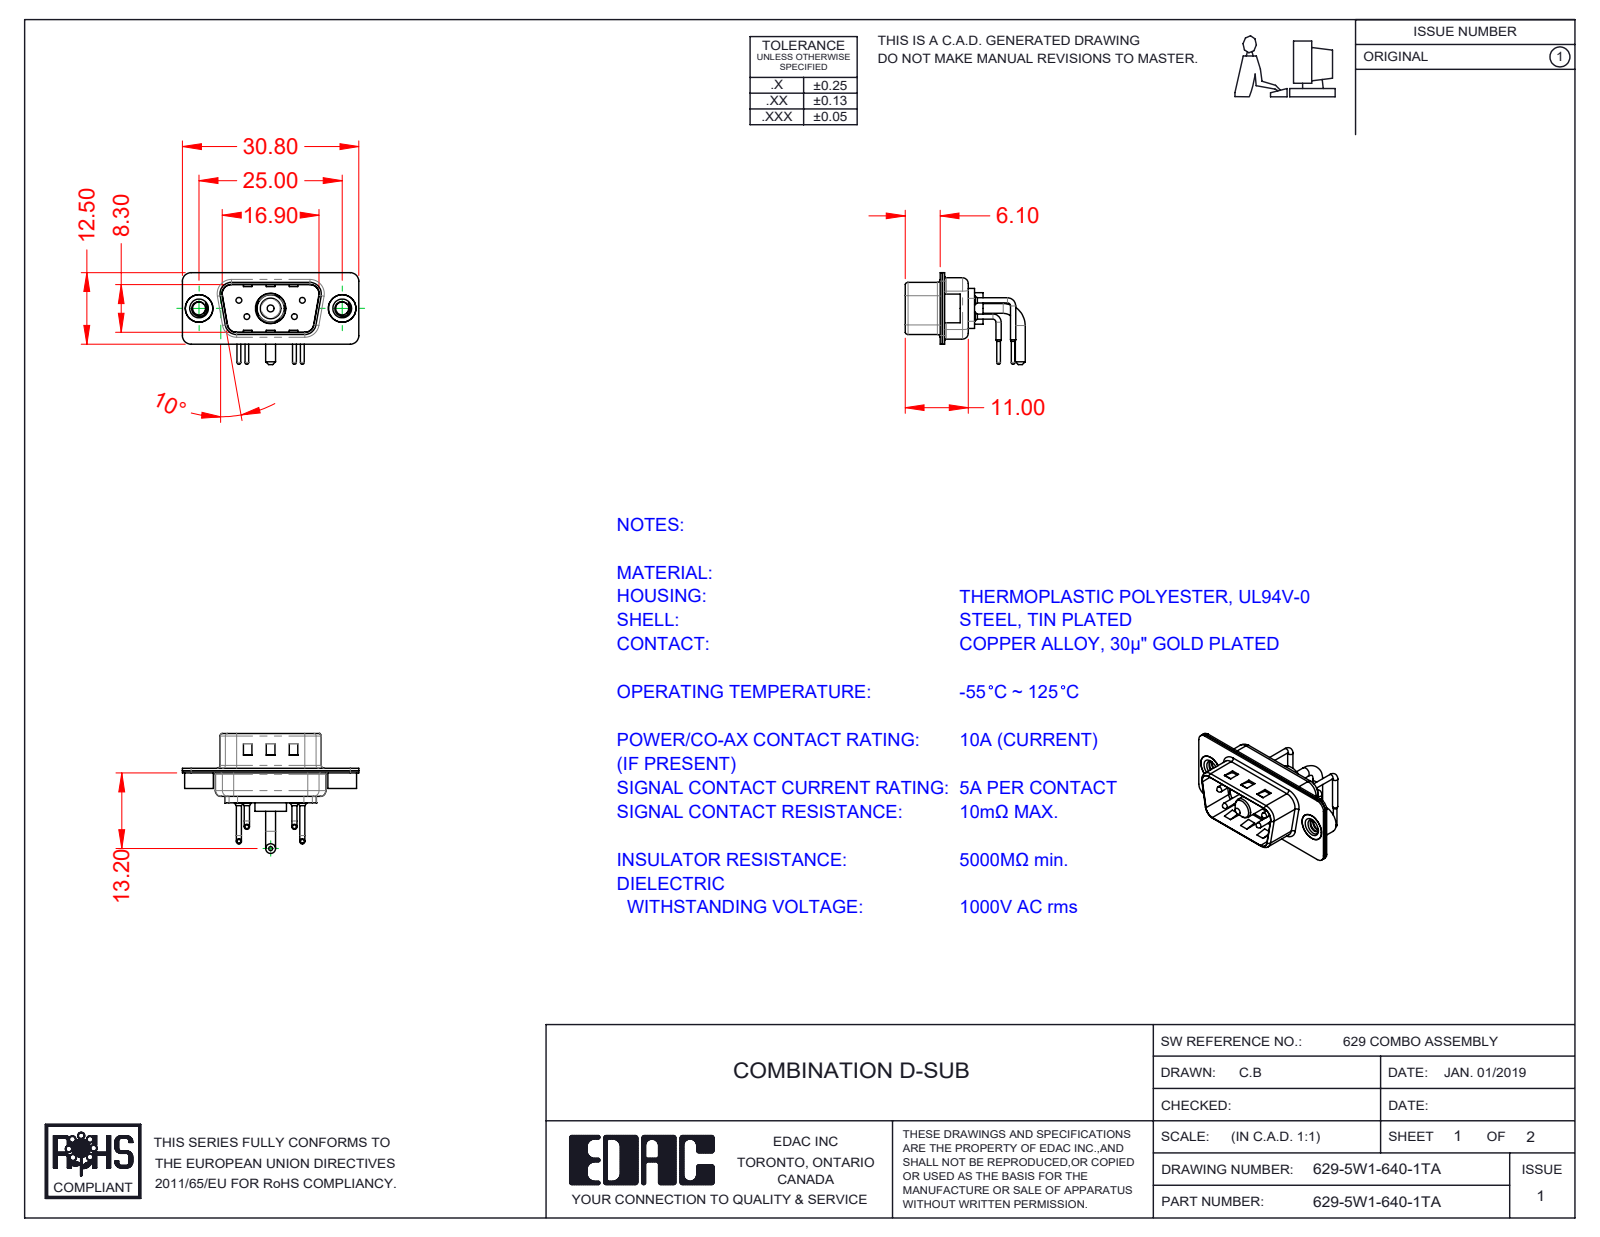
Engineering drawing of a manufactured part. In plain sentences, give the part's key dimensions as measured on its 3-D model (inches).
The part is named "629Combo Contact Row 1; 629Combo Shell Rear_09 Contacts; 629-5W1-640-1TA; Power Pin_10A RA (+4 more)". Its 3-D file was written by "SolidWorks 2020 (CONFIG_CONTROL_DESIGN)". It is 11 solids with 787 faces: 373 planar, 294 cylindrical and 120 other. Overall it measures 1.213 by 0.825 by 0.632 inches. Its volume is 0.087 cubic inches and its surface area 5.768 square inches. Round holes: 4 of diameter 0.03, 4 of diameter 0.063, 4 of diameter 0.079, 2 of diameter 0.089, 2 of diameter 0.157, 2 of diameter 0.189, 1 of diameter 0.191, 1 of diameter 0.209. Round bosses or shafts: 8 of diameter 0.035, 4 of diameter 0.059, 4 of diameter 0.039, 4 of diameter 0.026, 2 of diameter 0.197, 2 of diameter 0.193, 2 of diameter 0.067, 1 of diameter 0.217. Partial cylindrical surfaces (rounded edges, fillets, slot ends): 16 of radius 0.059, 12 of radius 0.079, 8 of radius 0.02, 8 of radius 0.063, 4 of radius 0.01, 4 of radius 0.024, 4 of radius 0.026, 4 of radius 0.035. The main face-to-face distances are 0.016, 0.031, 0.374, 0.358, 0.343, 0.39, 0.026, 0.22, 0.047, 0.03. The hole center spacings are 0.124, 0.225, 0.28, 0.492, 0.713, 0.173, 0.173, 0.327.
